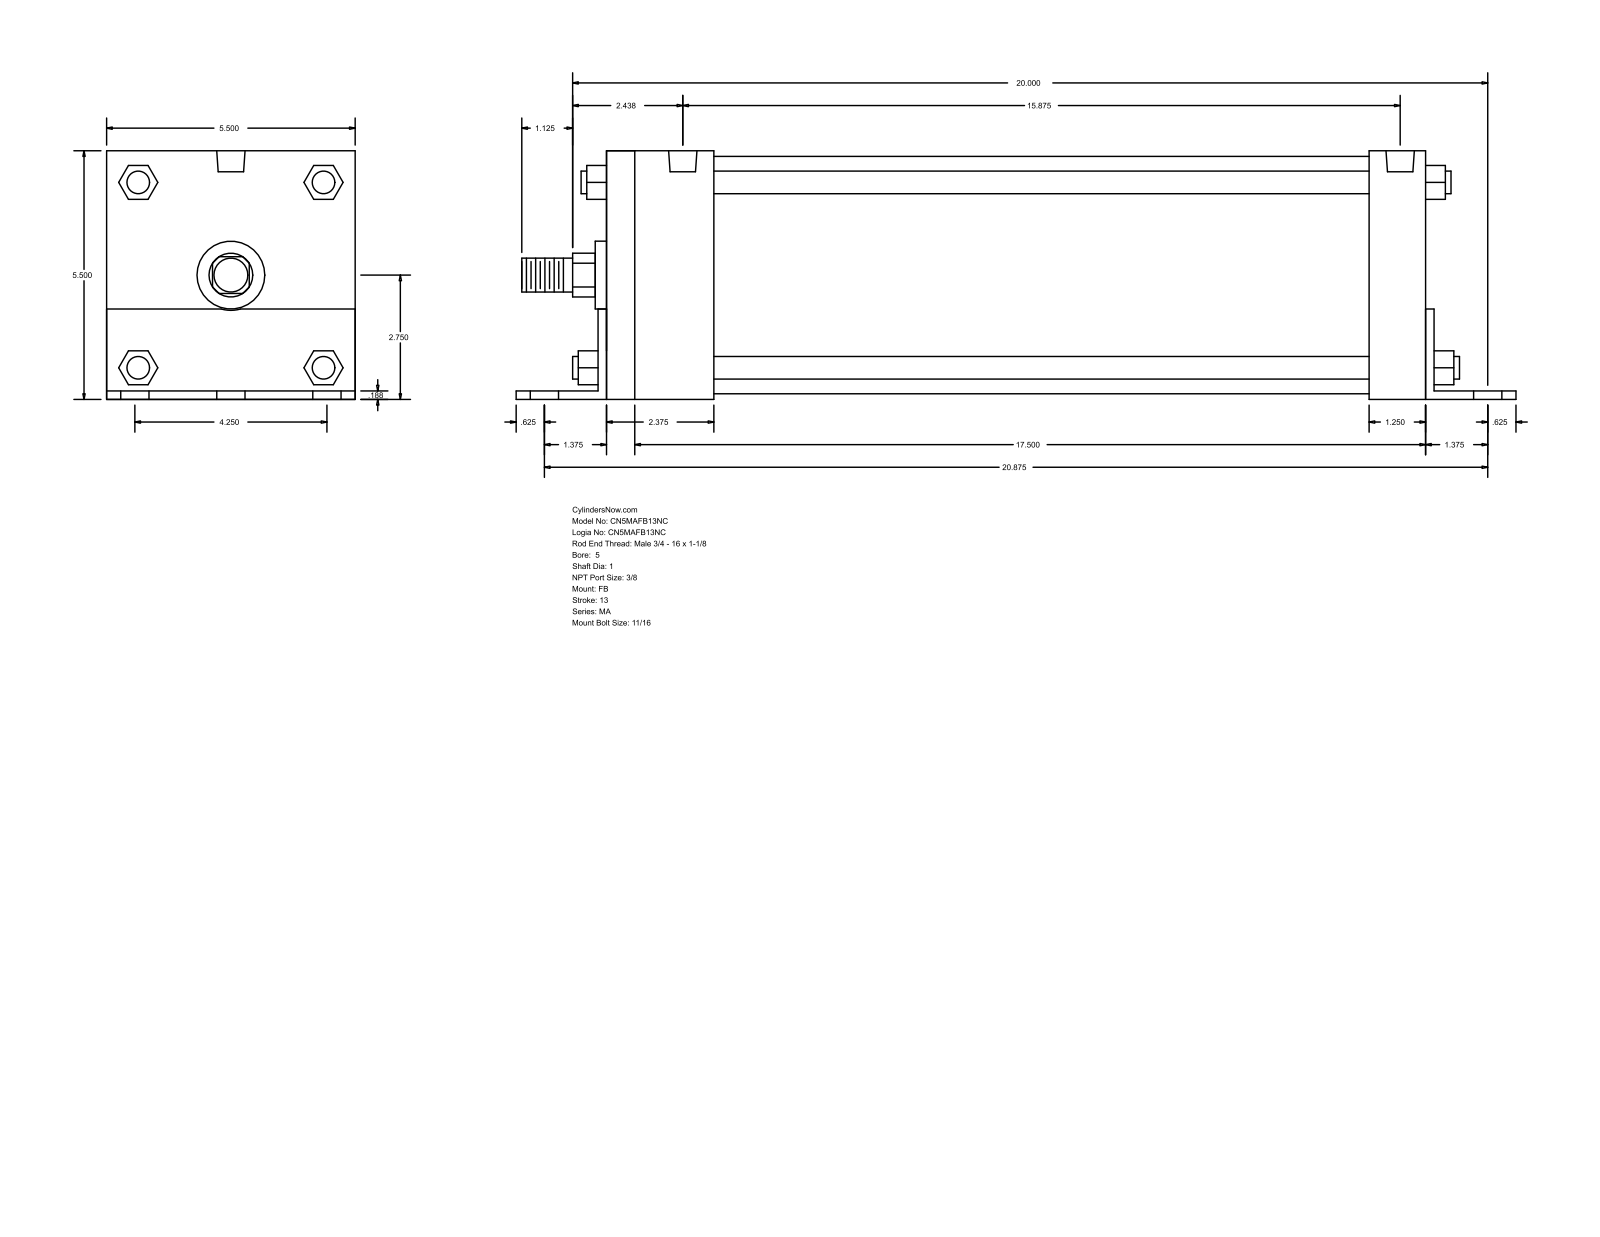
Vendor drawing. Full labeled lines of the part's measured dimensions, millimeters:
Part name (STEP PRODUCT): MA_FB__0500_1
STEP written by: GSSL Pune (CONFIG_CONTROL_DESIGN)
Units: millimetres
Bodies: 0 solids, 140 faces (105 planar, 35 cylindrical, 0 other)
Overall size (bounding box): 561.98 × 139.75 × 139.7
Round holes (diameter × count): ⌀17.46 ×6, ⌀11.11 ×4, ⌀15.93 ×2
Round bosses / shafts (diameter × count): ⌀12.7 ×4, ⌀133.35 ×1, ⌀38.1 ×1, ⌀25.4 ×1, ⌀19.05 ×1
Partial cylindrical surfaces — rounded edges, fillets, slot ends (radius × count): R12.29 ×1, R19.81 ×1
Main face-to-face distances: 139.7, 4.76, 139.75, 465.14, 4.71, 134.99, 460.38, 469.9, 31.75, 36.51
Hole centre spacings: 53.98, 532.97, 530.23, 4.76, 73.04, 76.33, 94.68, 98.63
